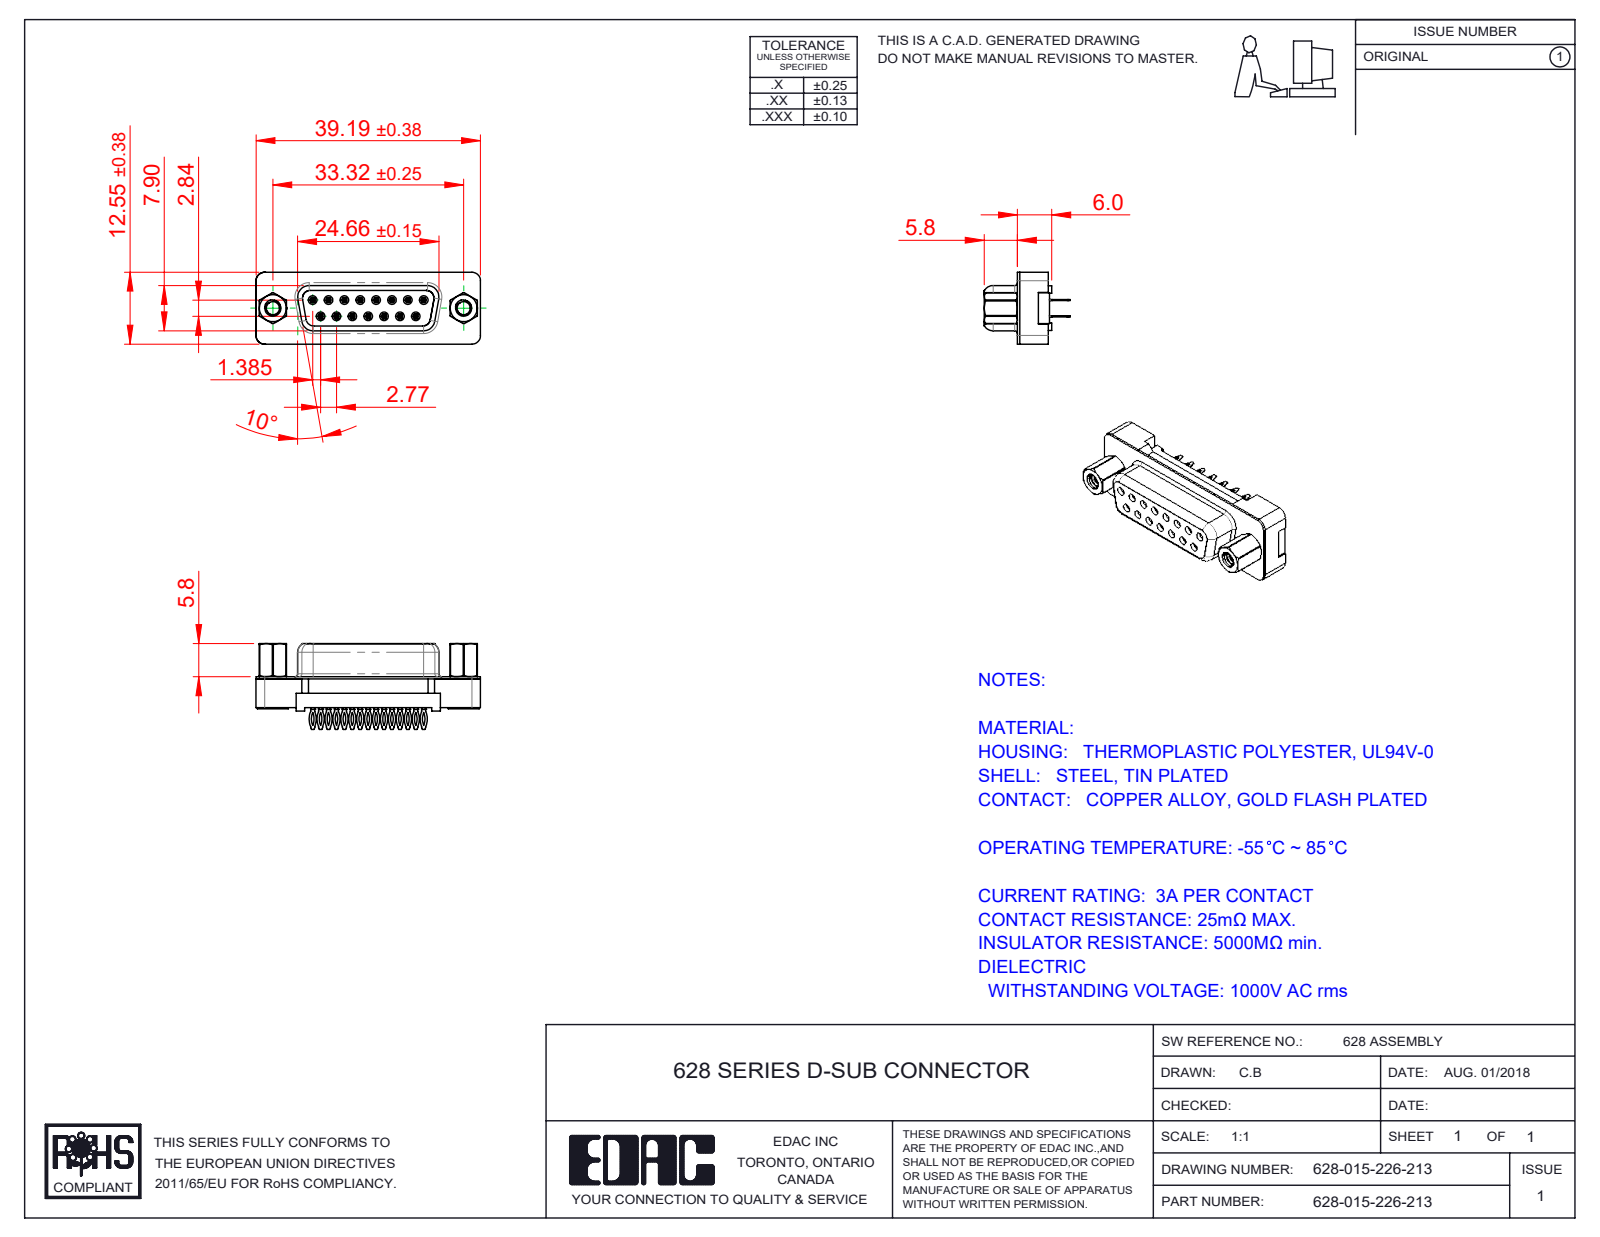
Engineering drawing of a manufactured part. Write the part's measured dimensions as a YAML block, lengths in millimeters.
part_name: "628 Plastic Body Housing_15 Contacts; 628-015-226-213; 628 PB Shell_15 Contacts; 628 4-40 Hex Standoff (+3 more)"
step_written_by: "SolidWorks 2020 (CONFIG_CONTROL_DESIGN)"
units: millimeters
bodies: {solids: 21, faces: 1721, planar: 676, cylindrical: 476, other: 569}
overall_size: [39.2, 15, 12.55]
volume: 2664
surface_area: 6386
round_holes:
  - {diameter: 0.9, count: 15}
  - {diameter: 2.26, count: 2}
  - {diameter: 2.29, count: 2}
  - {diameter: 3.05, count: 2}
  - {diameter: 4, count: 2}
  - {diameter: 4.8, count: 2}
  - {diameter: 5, count: 2}
round_bosses_or_shafts:
  - {diameter: 4.9, count: 2}
  - {diameter: 2.79, count: 2}
partial_cylinders:
  - {radius: 0.25, count: 60}
  - {radius: 2.92, count: 30}
  - {radius: 3.33, count: 30}
  - {radius: 0.5, count: 19}
  - {radius: 0.3, count: 15}
  - {radius: 1.35, count: 12}
  - {radius: 1.5, count: 8}
  - {radius: 0.9, count: 4}
face_to_face_distances: [0.4, 5.54, 2, 2.5, 6.2, 2.77, 0.68, 5.52, 2.68, 3.52]
hole_center_spacings: [3.16, 2.77, 5.54, 8.31, 11.08, 5.03, 5.04, 7.48]
